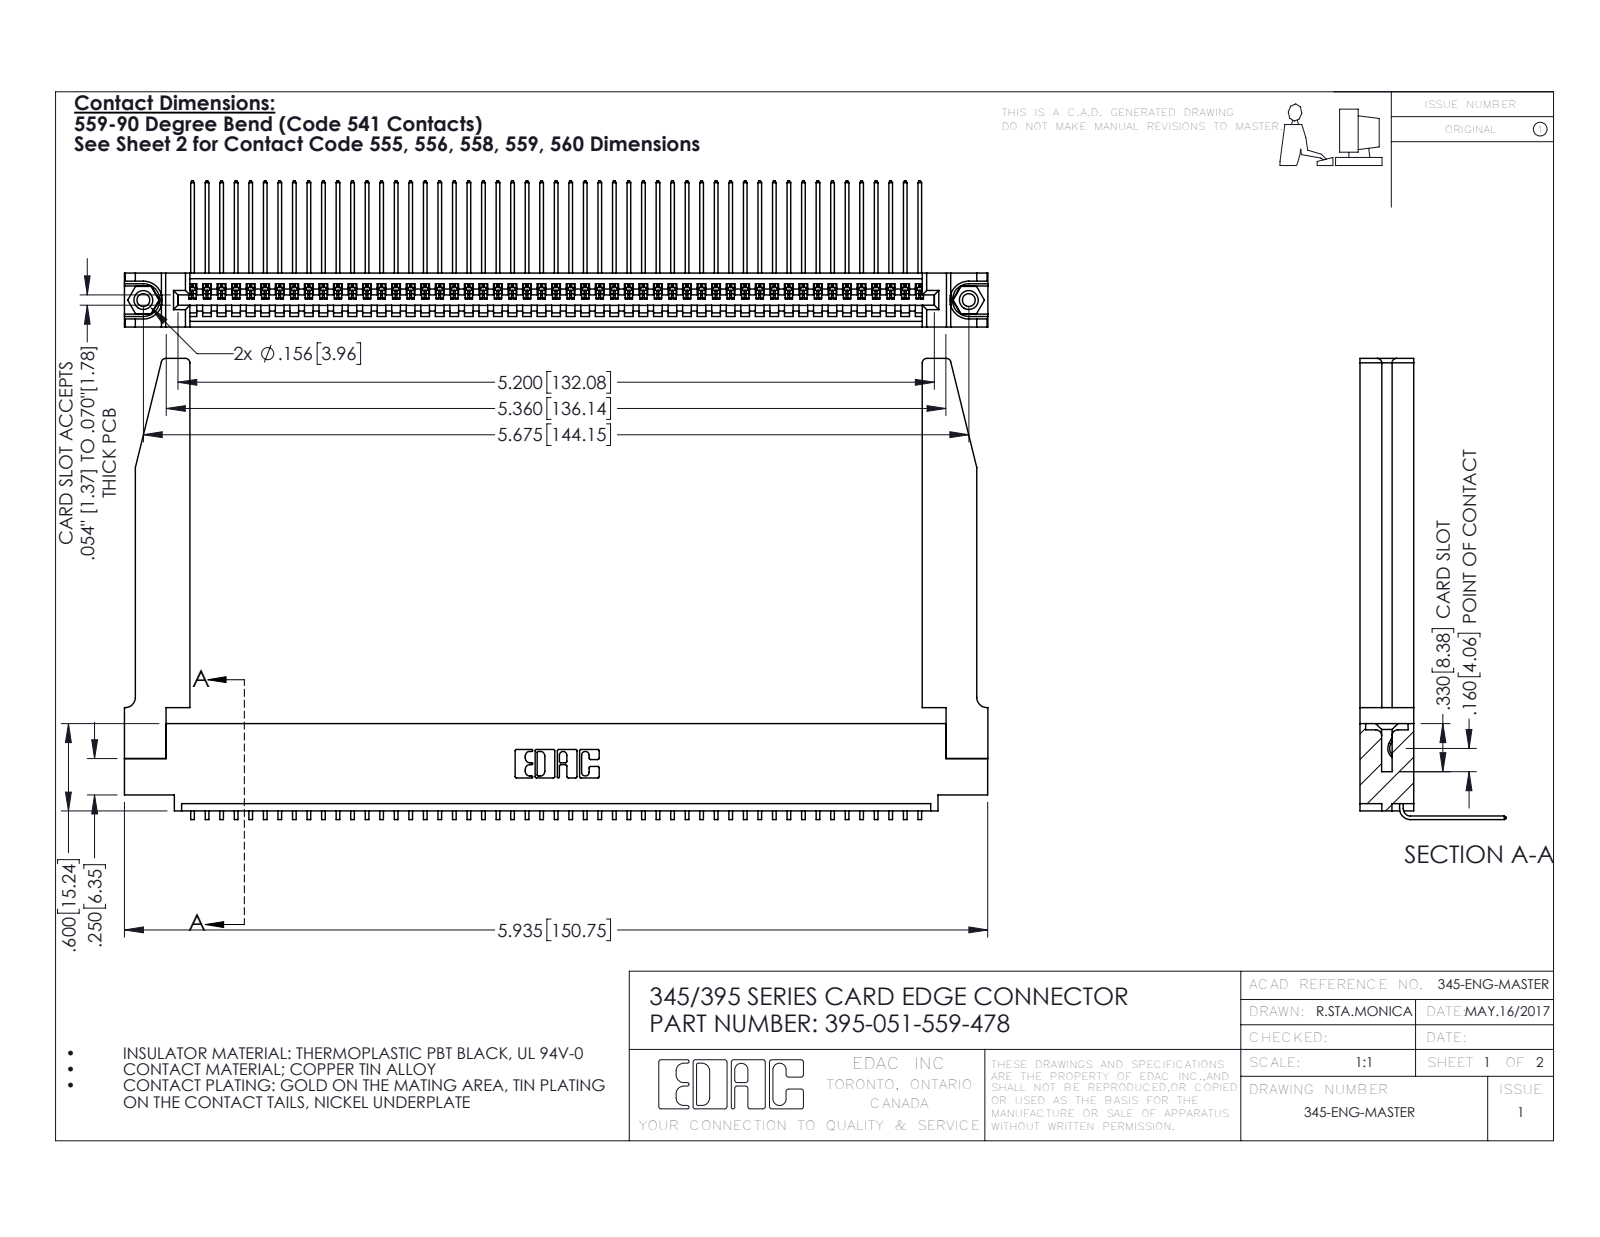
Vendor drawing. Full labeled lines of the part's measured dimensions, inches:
Part name (STEP PRODUCT): 345-292-001_558 559 Tail - 1; 345-220-078_345-220-078; 345 Part_0.110 Offset - 0.156 Dia-TH; 395-051-559-478 (+1 more)
STEP written by: SolidWorks 2016 (CONFIG_CONTROL_DESIGN)
Units: inches
Bodies: 56 solids, 3424 faces (2368 planar, 1004 cylindrical, 52 other)
Overall size (bounding box): 5.936 × 3.169 × 1.005
Volume: 1.358 in³ · Surface area: 42.32 in²
Round holes (diameter × count): ⌀0.089 ×2, ⌀0.125 ×2, ⌀0.156 ×2, ⌀0.064 ×1
Round bosses / shafts (diameter × count): ⌀0.155 ×2
Partial cylindrical surfaces — rounded edges, fillets, slot ends (radius × count): R0.006 ×102, R0.01 ×22, R0.03 ×8, R0.007 ×6, R0.031 ×6, R0.026 ×3, R0.031 ×2, R0.04 ×2
Main face-to-face distances: 0.37, 0.072, 0.298, 0.2, 0.098, 0.272, 0.025, 0.225, 0.148, 0.15
Hole centre spacings: 0.27, 5.439, 5.675
